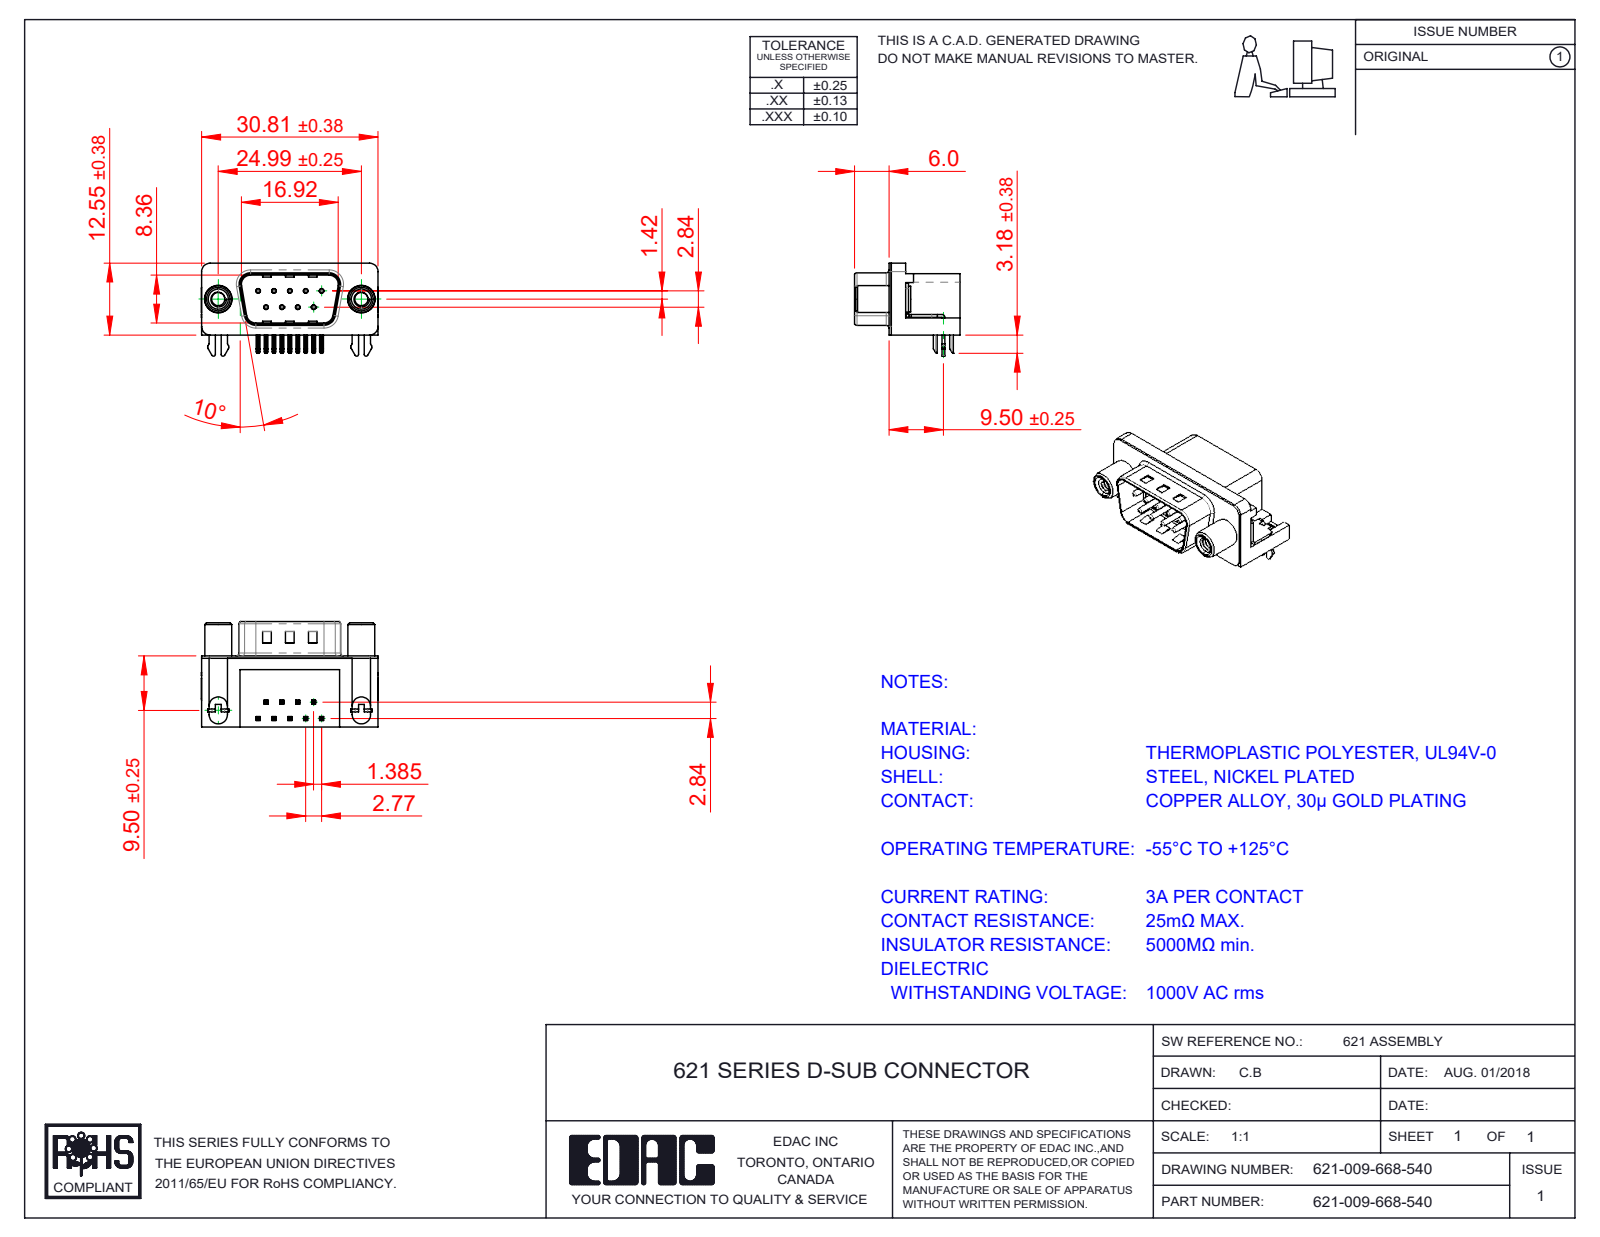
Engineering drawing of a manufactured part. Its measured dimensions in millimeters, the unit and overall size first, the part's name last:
Units: millimetres
Overall size (bounding box): 30.89 × 18.4 × 16.25
Round holes (diameter × count): ⌀0.35 ×9, ⌀0.8 ×9, ⌀2 ×2, ⌀2.3 ×2, ⌀3.1 ×2, ⌀4 ×2, ⌀4.8 ×2, ⌀5 ×2
Round bosses / shafts (diameter × count): ⌀0.75 ×9, ⌀4.9 ×2, ⌀4.7 ×2, ⌀4.5 ×2, ⌀3.85 ×2, ⌀3 ×2
Partial cylindrical surfaces — rounded edges, fillets, slot ends (radius × count): R0.25 ×40, R0.12 ×18, R1 ×16, R0.5 ×9, R1.5 ×8, R1.6 ×8, R0.9 ×4, R2 ×4
Main face-to-face distances: 0.4, 12, 12.4, 10.35, 9.5, 2.5, 2.9, 2.1, 0.35, 10.7
Hole centre spacings: 3.16, 2.77, 5.54, 5.03, 5.04, 8.31, 7.48, 7.49
Volume: 3 346 mm³ · Surface area: 4 695 mm²
Bodies: 15 solids, 1105 faces (607 planar, 329 cylindrical, 169 other)
Part name (STEP PRODUCT): 621-009-668-540; 621 Housing_9 Socket; 621 Round Threaded Standoff; 621 Contact Top (+3 more)
STEP written by: SolidWorks 2016 (CONFIG_CONTROL_DESIGN)
